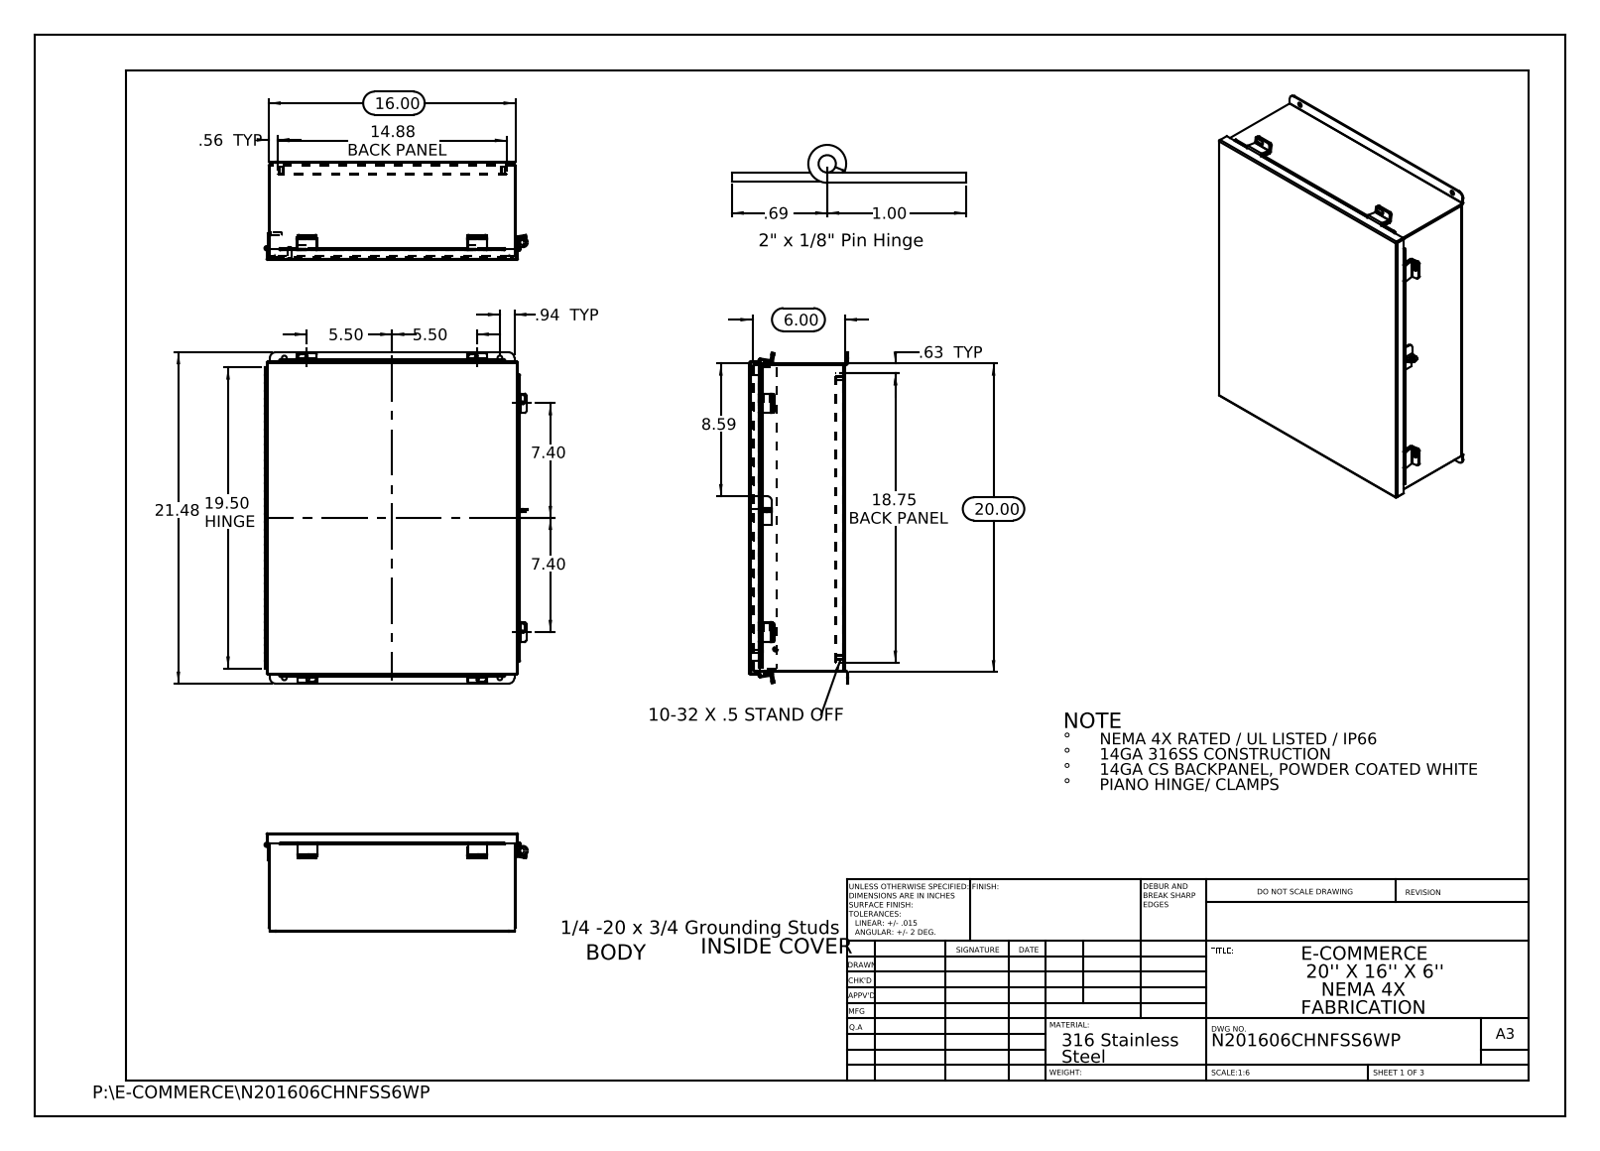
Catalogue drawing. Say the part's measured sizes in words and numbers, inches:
The part is named "N201606CHNFSS6WP _JIC Hinge; N201606CHNFSS6WP JIC Enclosure Template; N201606CHNFSS6WP JIC_Cover_Template; N201606CHNFSS6WP Hinge Cover Side JIC (+8 more)". Its 3-D file was written by "SolidWorks 2013 (CONFIG_CONTROL_DESIGN)". It is 27 solids with 938 faces: 579 planar, 339 cylindrical and 20 other. Overall it measures 21.476 by 17.072 by 6.39 inches. Its volume is 113 cubic inches and its surface area 3 067 square inches. Round holes: 10 of diameter 0.25, 4 of diameter 0.187, 4 of diameter 0.312, 1 of diameter 0.125, 1 of diameter 0.125, 1 of diameter 0.373, 1 of diameter 0.375. Round bosses or shafts: 4 of diameter 0.313, 2 of diameter 0.315, 2 of diameter 0.236, 1 of diameter 0.273, 1 of diameter 0.25. Partial cylindrical surfaces (rounded edges, fillets, slot ends): 21 of radius 0.125, 13 of radius 0.013, 12 of radius 0.009, 12 of radius 0.088, 12 of radius 0.133, 6 of radius 0.083, 6 of radius 0.1, 4 of radius 0.375. The main face-to-face distances are 0.075, 6.128, 6.053, 6.203, 0.074, 5.628, 0.575, 0.5, 5.553, 0.649. The hole center spacings are 1.315, 14.235, 19.427, 24.048, 11, 13.976, 14.375, 18.126.
